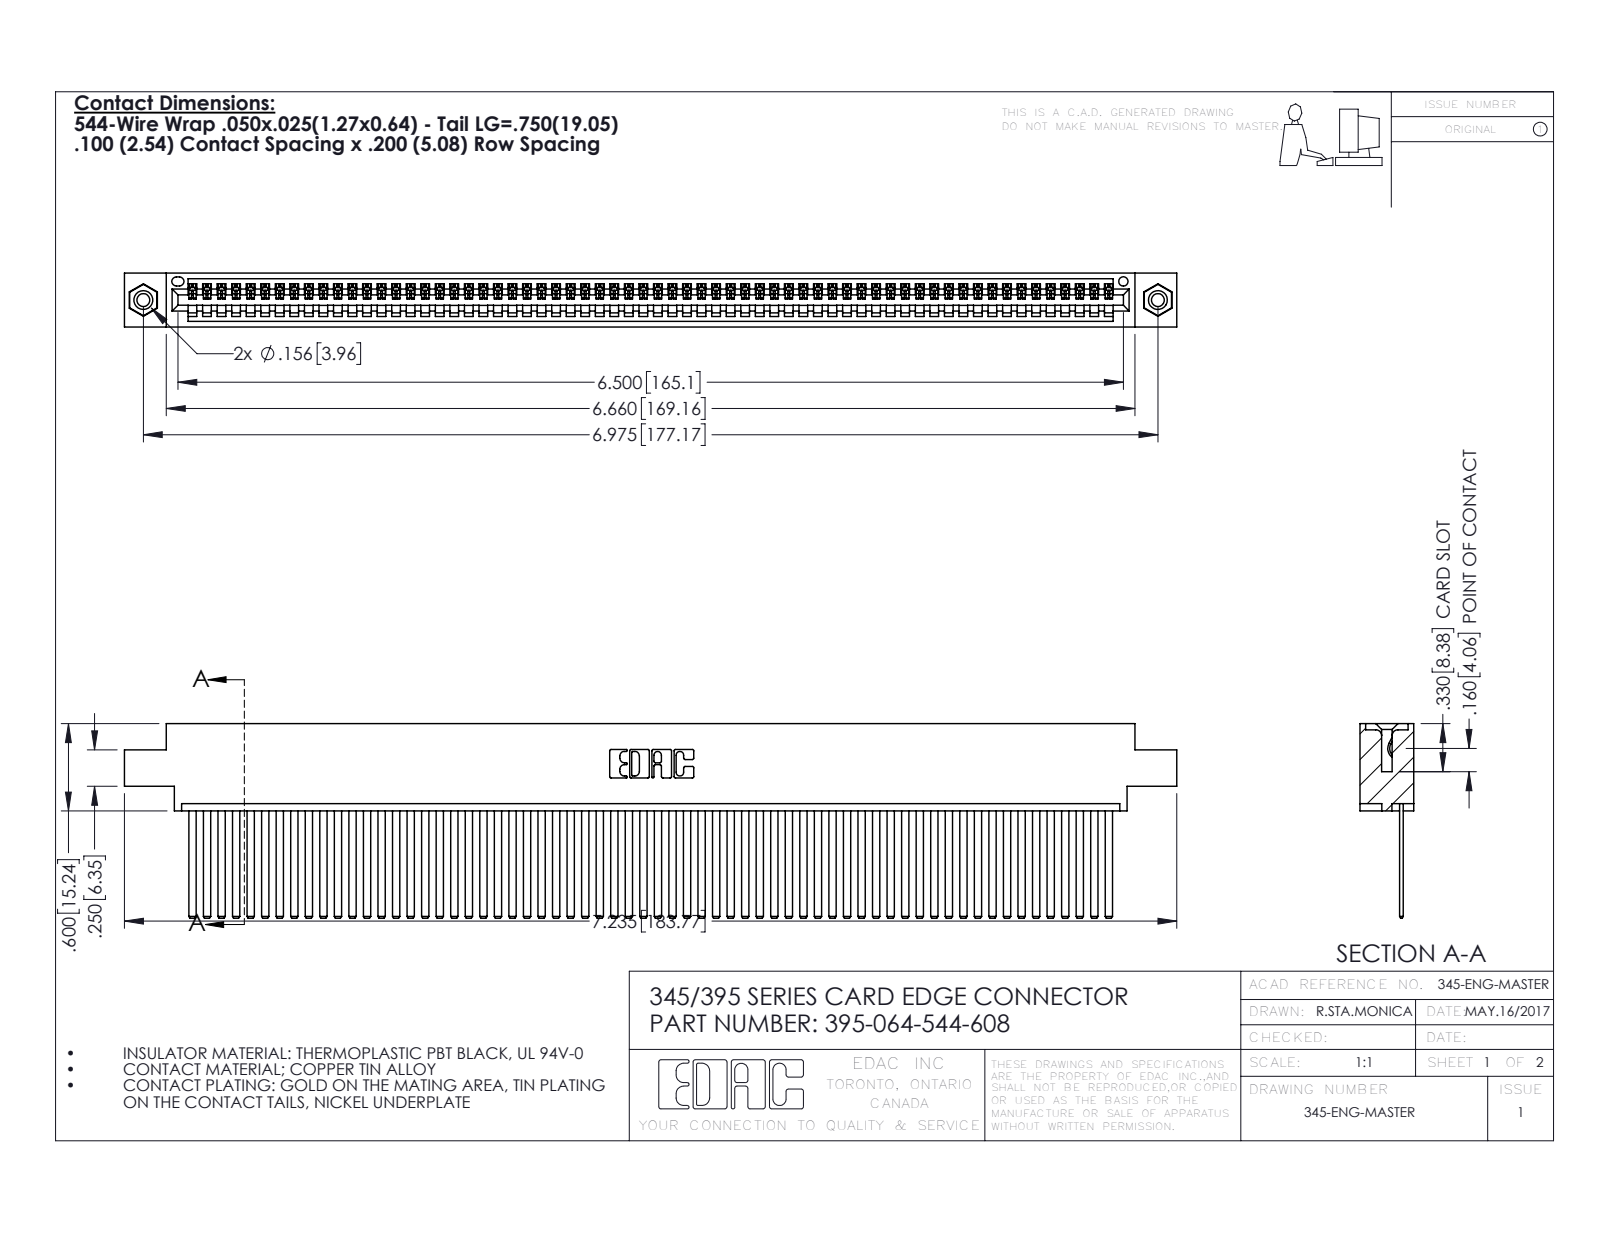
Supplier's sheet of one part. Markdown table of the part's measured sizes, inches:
| quantity | value |
| --- | --- |
| part name | 345 Part_0.170 Offset - 0.156 Dia-TI; 395-064-544-608; 345-292-001_345-293-144; 345-250-001_345-250-003-102 |
| STEP written by | SolidWorks 2016 (CONFIG_CONTROL_DESIGN) |
| units | inches |
| bodies | 67 solids, 3518 faces (2420 planar, 1082 cylindrical, 16 other) |
| overall size | 7.235 × 1.337 × 0.37 |
| volume | 1.114 in³ |
| surface area | 41.74 in² |
| round holes (diameter × count) | 0.089 × 2, 0.125 × 2, 0.156 × 2, 0.064 × 1 |
| round bosses / shafts (diameter × count) | 0.155 × 2 |
| partial cylindrical surfaces (radius × count) | 0.006 × 128, 0.01 × 22, 0.007 × 6, 0.031 × 6, 0.026 × 3, 0.031 × 2, 0.04 × 2, 0.014 × 1 |
| main face-to-face distances | 0.072, 0.298, 0.025, 0.098, 0.272, 0.37, 0.2, 0.225, 0.175, 0.149 |
| hole center spacings | 0.27, 6.739, 6.975 |
